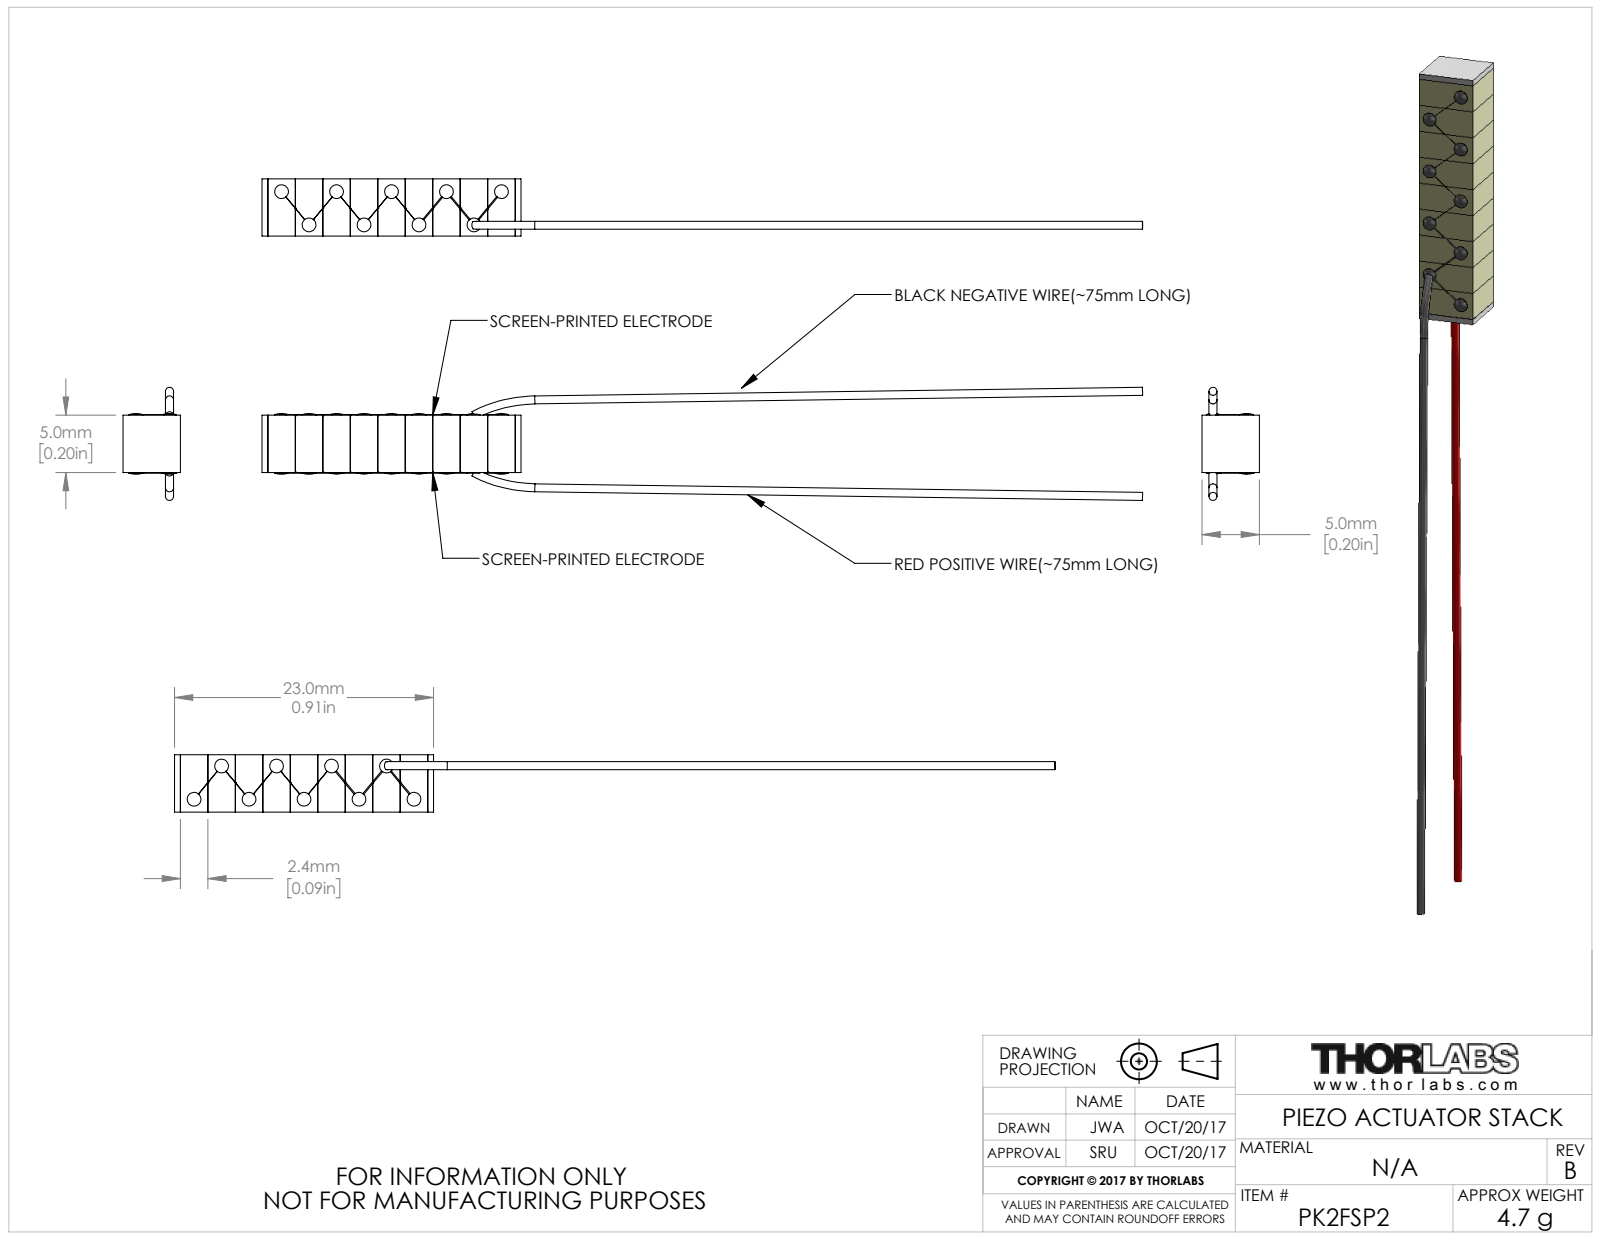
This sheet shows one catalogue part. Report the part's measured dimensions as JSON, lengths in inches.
{"part_name": "CTN002569", "step_written_by": "SolidWorks 2016 (AUTOMOTIVE_DESIGN)", "units": "inches", "bodies": {"solids": 3, "faces": 211, "planar": 85, "cylindrical": 72, "other": 54}, "overall_size": [3.027, 0.389, 0.197], "volume_in3": 0.037, "surface_area_in2": 1.961, "round_bosses_or_shafts": [[0.047, 9], [0.028, 2]], "face_to_face_distances": [0.094, 0.189, 0.283, 0.378, 0.472, 0.197, 0.567, 0.661, 0.756, 0.02]}
